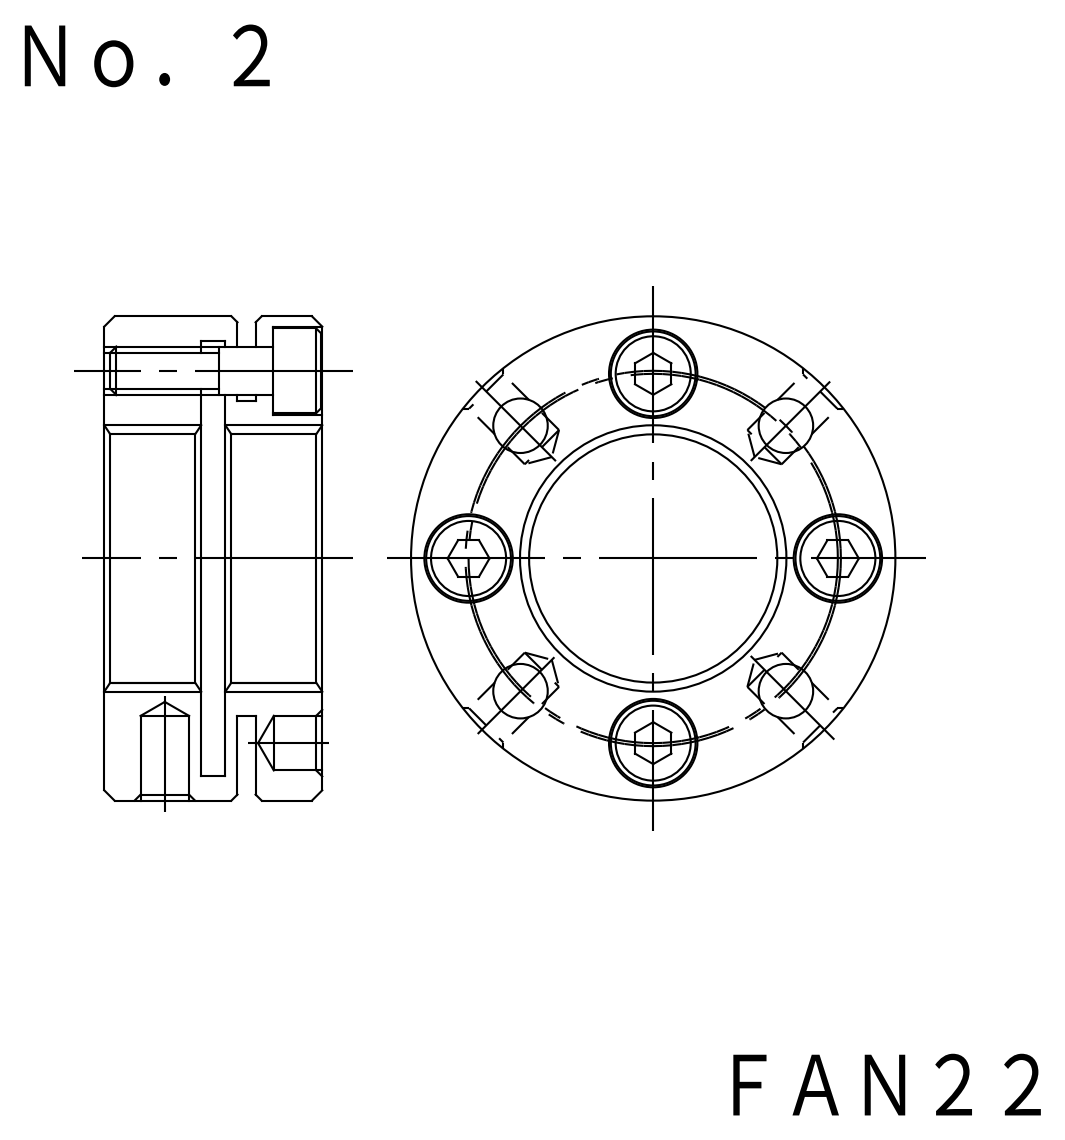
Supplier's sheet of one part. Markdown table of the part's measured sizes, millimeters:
| quantity | value |
| --- | --- |
| part name | FKD FAN22; M4X12_default |
| STEP written by | SolidWorks 2012 (CONFIG_CONTROL_DESIGN) |
| units | millimeters |
| bodies | 5 solids, 142 faces (50 planar, 76 cylindrical, 16 other) |
| overall size | 40 × 40 × 18 |
| volume | 12 864 mm³ |
| surface area | 10 433 mm² |
| round holes (diameter × count) | 3.24 × 4, 4.3 × 4, 4.5 × 4, 7.3 × 4, 4 × 2, 22 × 1, 35.5 × 1 |
| round bosses / shafts (diameter × count) | 7 × 4, 4 × 4, 40 × 1, 25.5 × 1 |
| main face-to-face distances | 8, 10, 11, 12.5, 1.5, 18, 7, 5.5, 2, 3 |
| hole center spacings | 11.67, 15.25, 28.17, 21.56, 21.57, 30.49, 30.5 |
